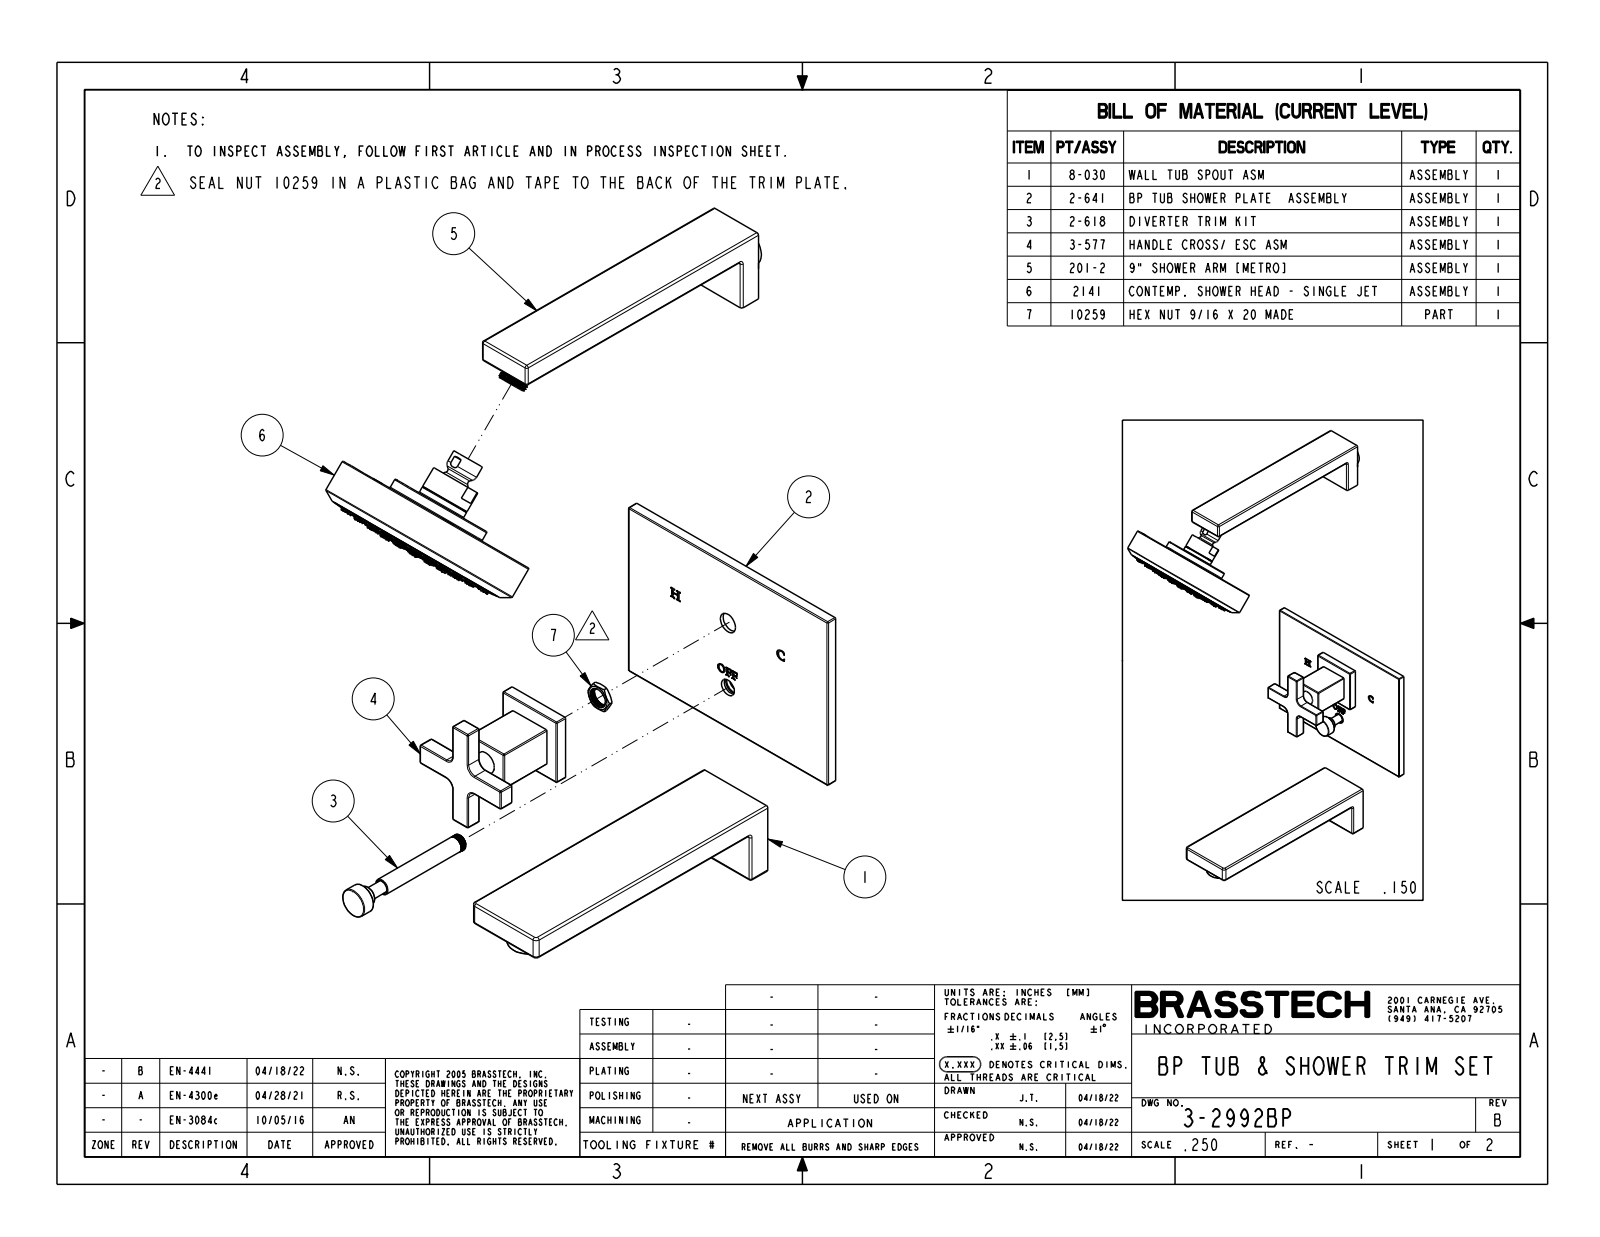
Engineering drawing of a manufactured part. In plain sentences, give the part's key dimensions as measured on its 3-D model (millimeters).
The part is named "3-2992BP". Its 3-D file was written by "CREO PARAMETRIC BY PTC INC, 2018400 (CONFIG_CONTROL_DESIGN)". It is 3 solids with 1259 faces: 196 planar, 296 cylindrical and 767 other. Overall it measures 541 by 317.3 by 196.9 millimeters. Its volume is 1 380 000 cubic millimeters and its surface area 212 600 square millimeters. Round holes: 90 of diameter 1.3, 1 of diameter 5.6, 1 of diameter 133.5. Round bosses or shafts: 2 of diameter 35.6, 1 of diameter 150.1, 1 of diameter 132.6, 1 of diameter 74.2, 1 of diameter 45.7, 1 of diameter 31.8, 1 of diameter 23, 1 of diameter 21.3. Partial cylindrical surfaces (rounded edges, fillets, slot ends): 48 of radius 0.8, 21 of radius 1.5, 4 of radius 6.4, 2 of radius 2, 2 of radius 3, 1 of radius 12.1. The main face-to-face distances are 7.9, 17, 485.1, 16.6, 502.2, 485.5, 468.5, 9.5, 54, 63.5. The hole center spacings are 46.7, 57.7, 12.2, 24.2, 12, 35.8, 56.9, 24.
